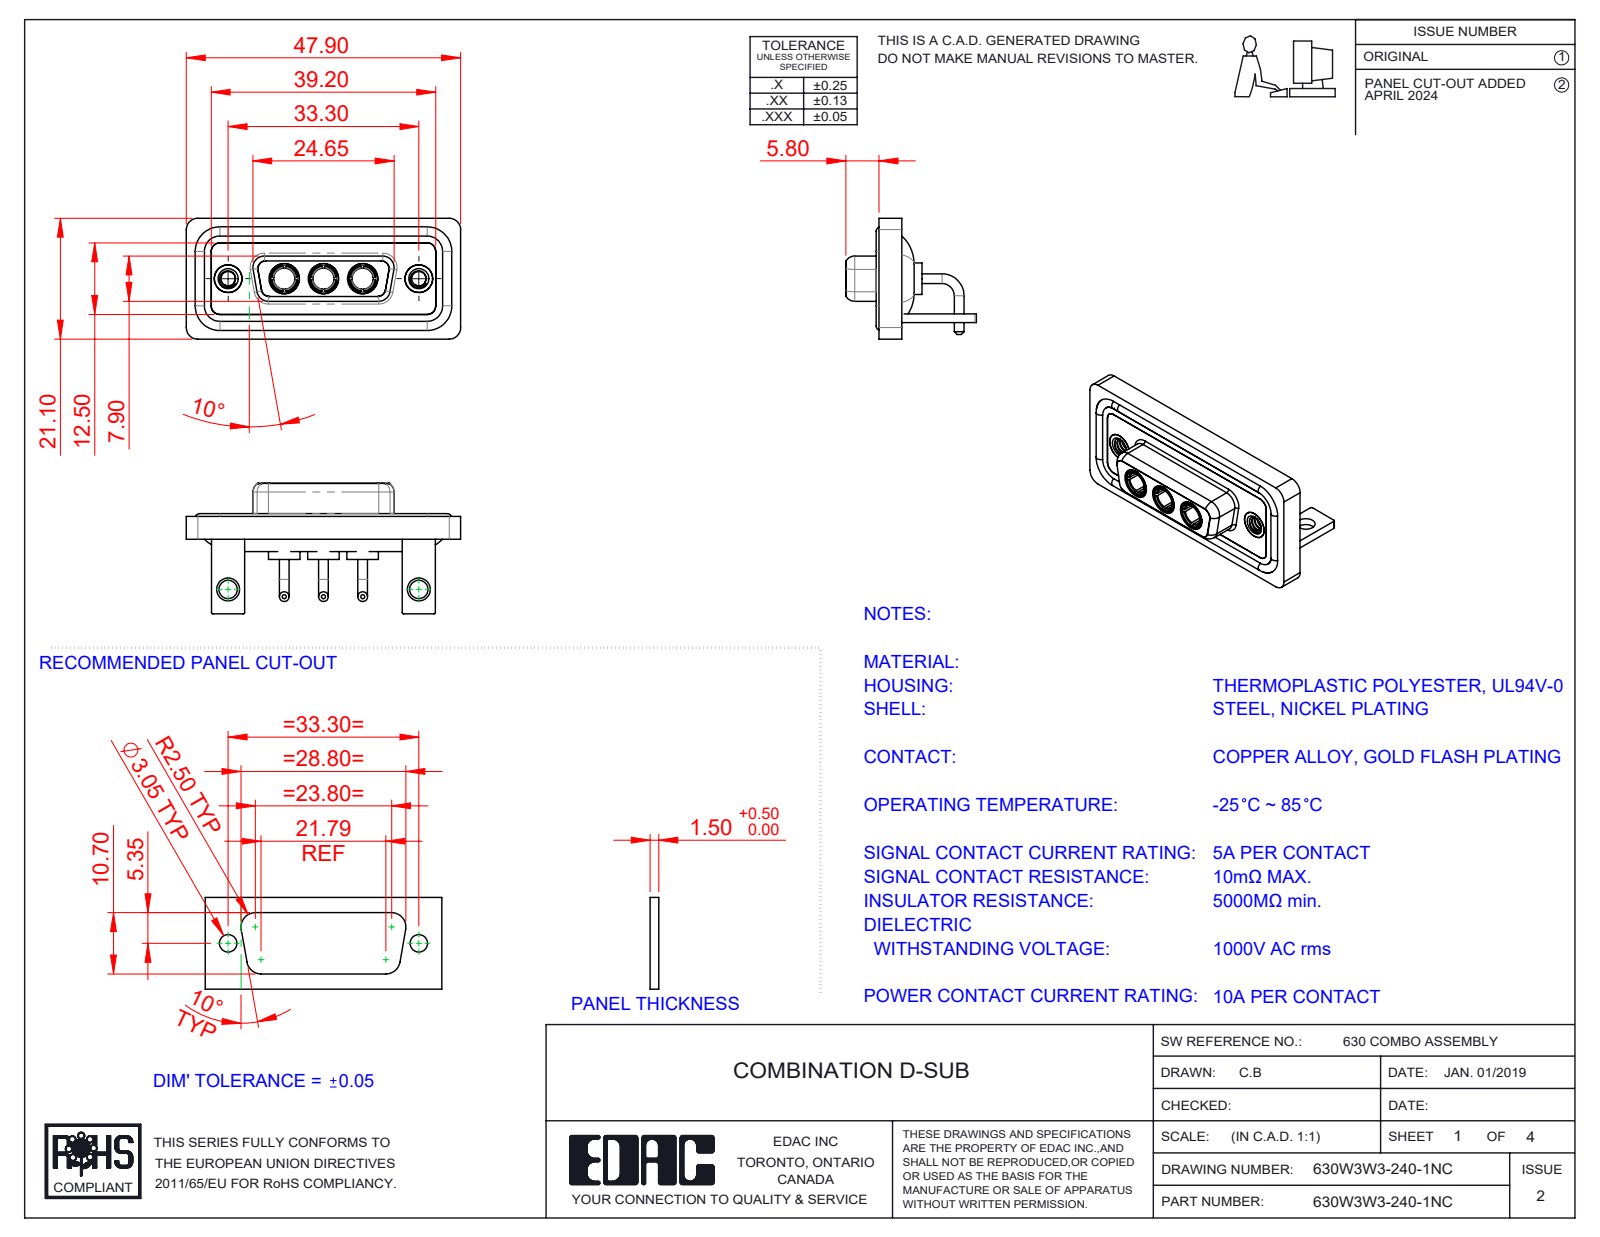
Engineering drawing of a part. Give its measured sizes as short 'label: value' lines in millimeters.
name: Power Socket_10A RA; 630W3W3-140-1NC; 630Combo Waterproof Housing_15 Contacts; 630Combo Threaded Rivet_A (+4 more)
written by: SolidWorks 2023 (CONFIG_CONTROL_DESIGN)
unit: mm
bodies: 15 solids, 662 faces (212 planar, 285 cylindrical, 165 other)
size: 47.9 × 22.8 × 21.1
volume: 6 366 mm³; area: 10 558 mm²
holes: 5× ⌀4.85, 3× ⌀3.7, 3× ⌀5.3, 2× ⌀2.5, 2× ⌀3.2, 2× ⌀4, 2× ⌀4.05, 2× ⌀5
bosses: 6× ⌀1.7, 4× ⌀1.6, 3× ⌀5.5, 3× ⌀5.2, 3× ⌀4.96, 3× ⌀4.75, 3× ⌀3.75, 2× ⌀4.95
rounds: 21× R2, 18× R1.5, 16× R0.25, 12× R1.35, 8× R1.6, 5× R0.5, 4× R0.6, 4× R0.65
face distances: 0.4, 2.9, 1.5, 1.8, 3.7, 1.1, 4.1, 1.6, 2.5, 1.4
hole spacings: 6.85, 9.8, 16.65, 23.5, 33.3, 13.7
